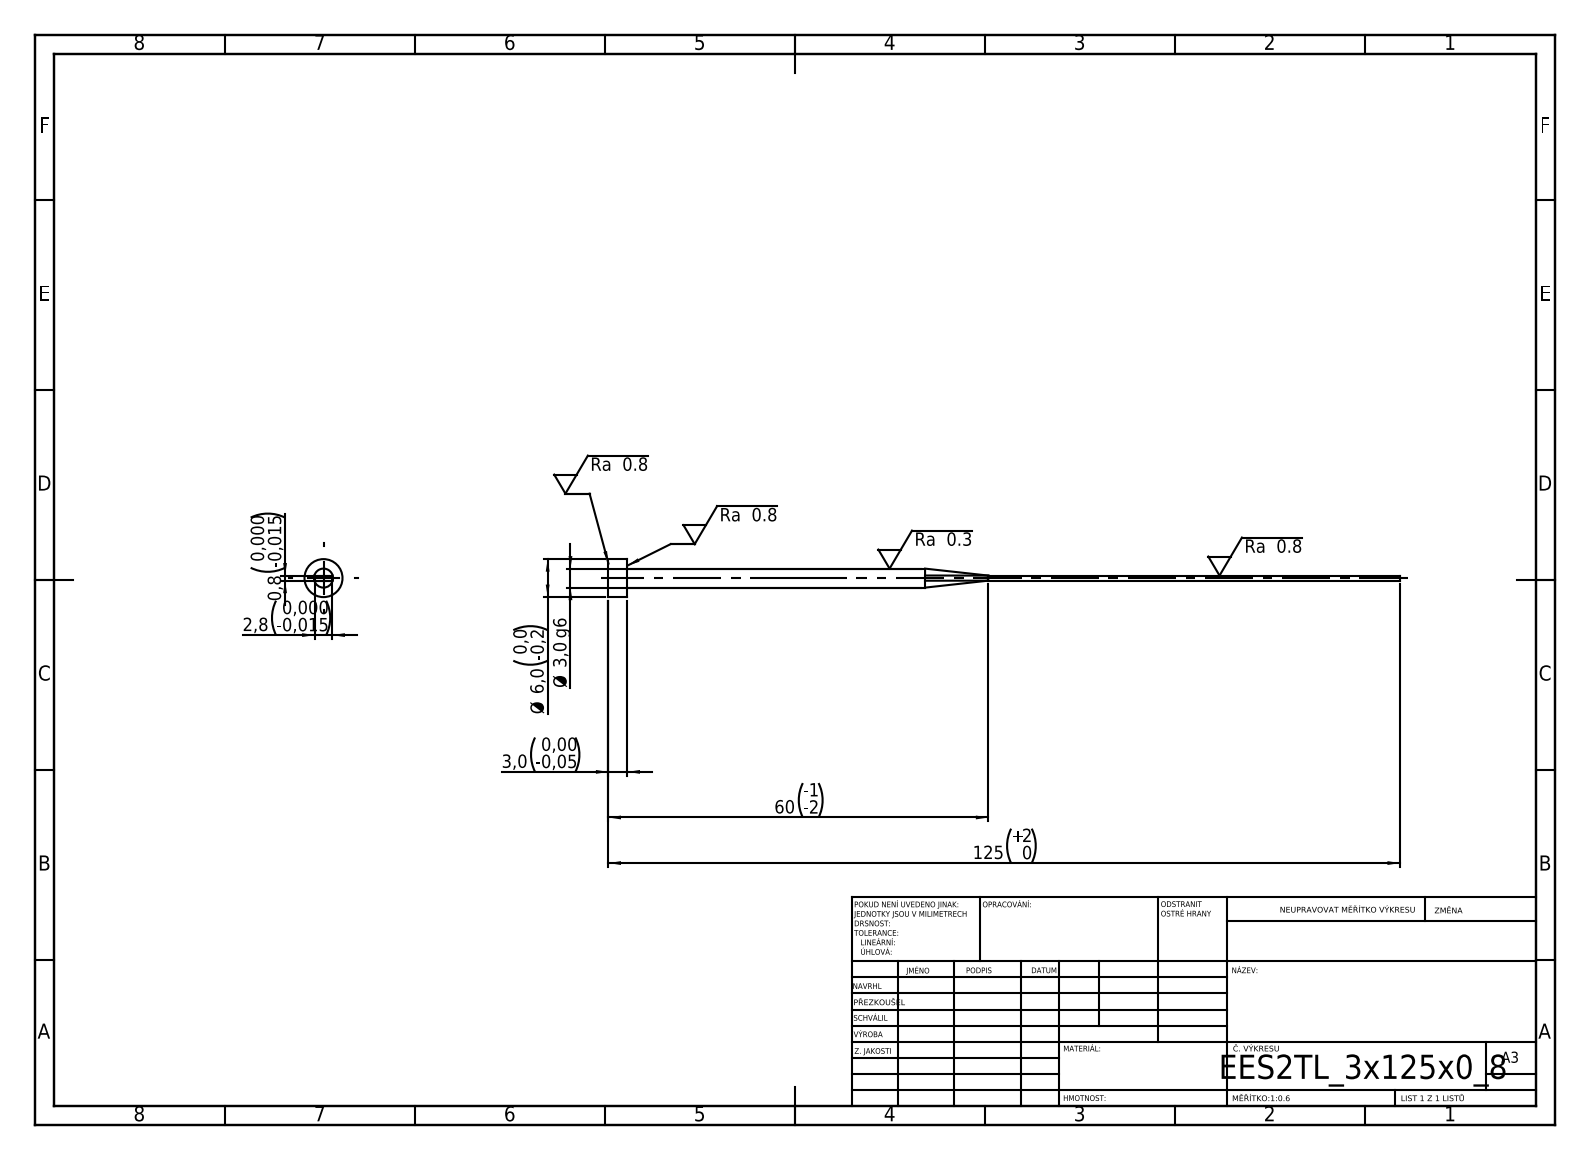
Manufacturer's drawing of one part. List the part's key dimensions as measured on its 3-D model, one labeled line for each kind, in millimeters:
STEP written by: SolidWorks 2019 (CONFIG_CONTROL_DESIGN)
Units: millimetres
Bodies: 1 solid, 15 faces (7 planar, 4 cylindrical, 4 other)
Overall size (bounding box): 125 × 6 × 6
Volume: 608 mm³ · Surface area: 1 099 mm²
Round bosses / shafts (diameter × count): ⌀6 ×1, ⌀3 ×1
Main face-to-face distances: 0.8, 2.8, 3, 125, 122
